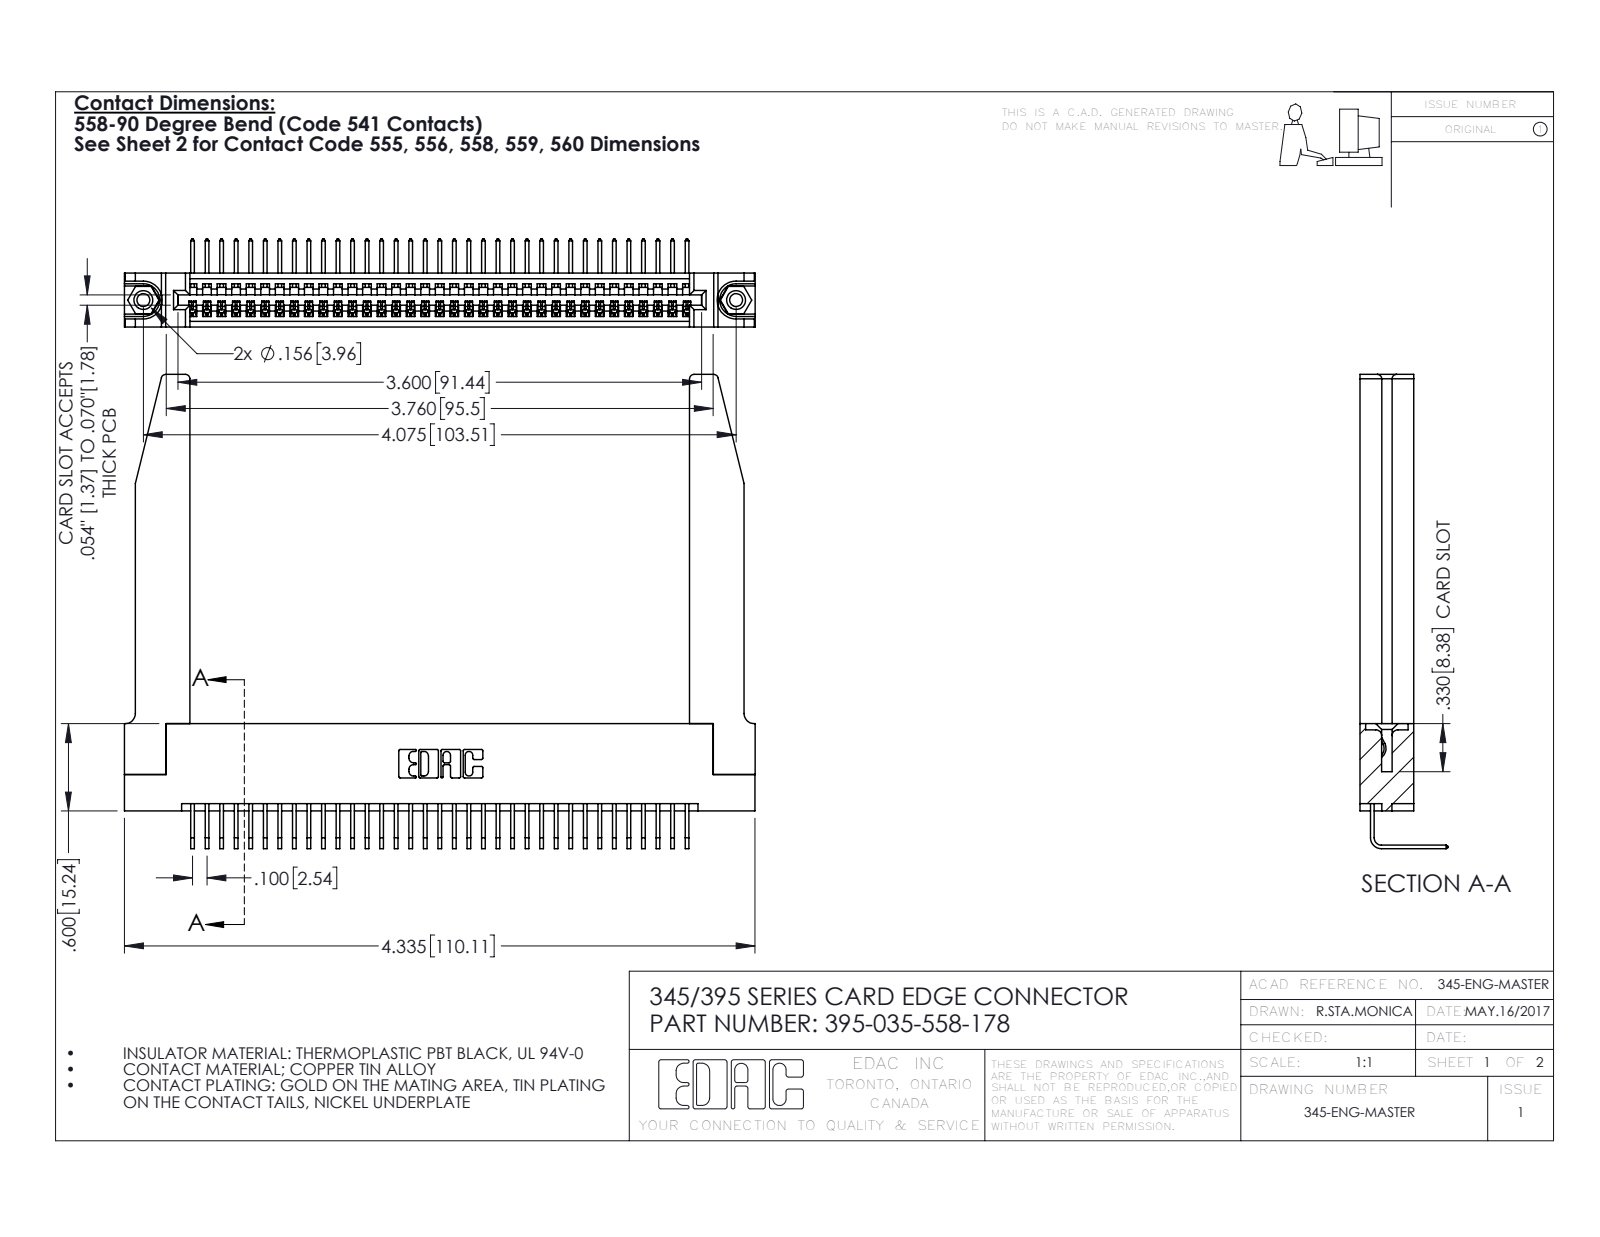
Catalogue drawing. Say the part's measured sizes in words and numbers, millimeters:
The part is named "345-220-078_345-220-078; 345-250-001_345-250-001-102; 395-035-558-178; 345-292-001_558 Tail - 2 (+1 more)". Its 3-D file was written by "SolidWorks 2016 (CONFIG_CONTROL_DESIGN)". It is 40 solids with 2460 faces: 1692 planar, 716 cylindrical and 52 other. Overall it measures 110.1 by 82.8 by 15.4 millimeters. Its volume is 18 290 cubic millimeters and its surface area 21 410 square millimeters. Round holes: 2 of diameter 2.3, 2 of diameter 3.2, 2 of diameter 4, 1 of diameter 1.6. Round bosses or shafts: 2 of diameter 3.9. Partial cylindrical surfaces (rounded edges, fillets, slot ends): 70 of radius 0.2, 22 of radius 0.3, 8 of radius 0.8, 6 of radius 0.2, 6 of radius 0.8, 3 of radius 0.7, 2 of radius 0.8, 2 of radius 1. The main face-to-face distances are 9.4, 1.8, 7.6, 5.1, 2.5, 6.9, 0.6, 5.7, 3.8, 3.8. The hole center spacings are 6.9, 97.5, 103.5.
